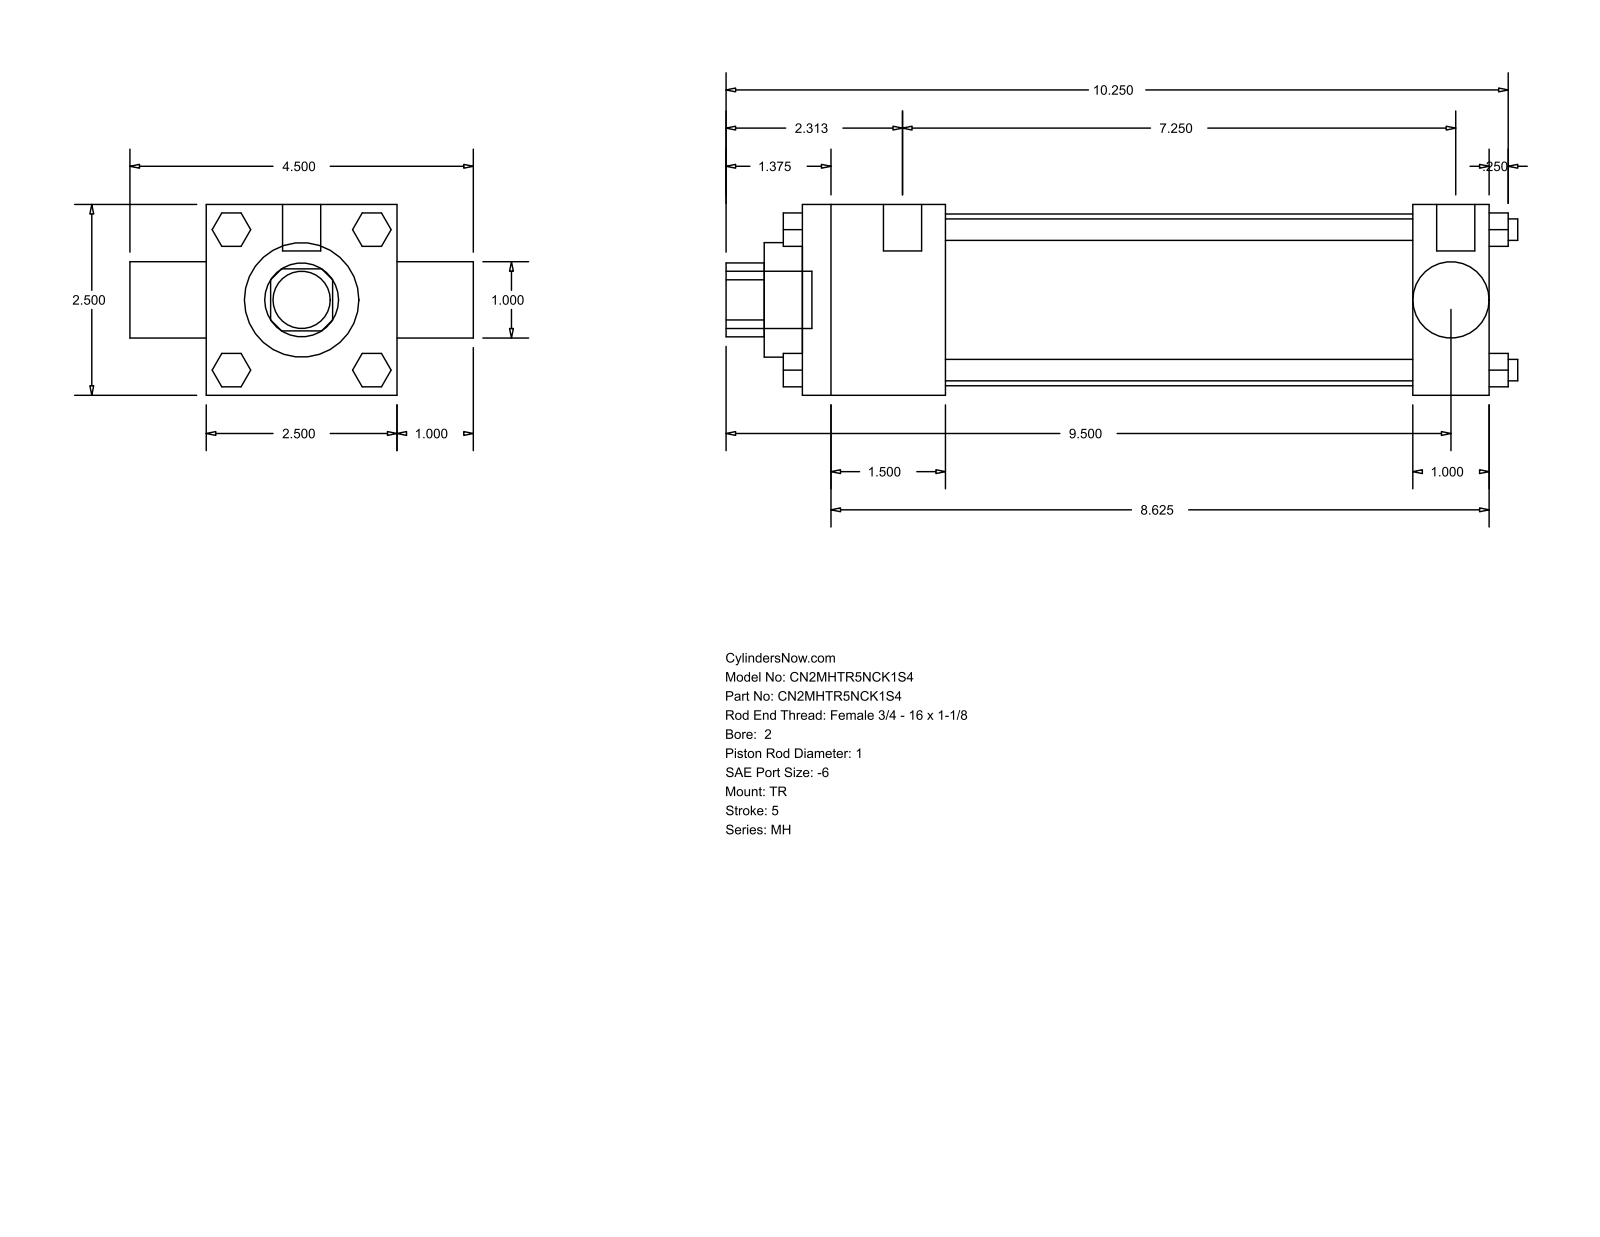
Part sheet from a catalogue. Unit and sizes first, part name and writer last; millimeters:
Units: millimetres
Overall size (bounding box): 263.52 × 114.3 × 63.5
Round holes (diameter × count): ⌀25.35 ×1, ⌀25.4 ×1, ⌀38.1 ×1, ⌀57.15 ×1
Round bosses / shafts (diameter × count): ⌀7.14 ×4, ⌀5.56 ×3, ⌀12.7 ×2, ⌀19.05 ×1
Partial cylindrical surfaces — rounded edges, fillets, slot ends (radius × count): R12.29 ×1
Main face-to-face distances: 63.5, 228.6, 25.4, 47.63, 203.2, 155.57, 180.97, 88.9, 241.3, 6.35
Bodies: 0 solids, 120 faces (92 planar, 28 cylindrical, 0 other)
Part name (STEP PRODUCT): MH_TR__0200_1
STEP written by: GSSL Pune (CONFIG_CONTROL_DESIGN)
